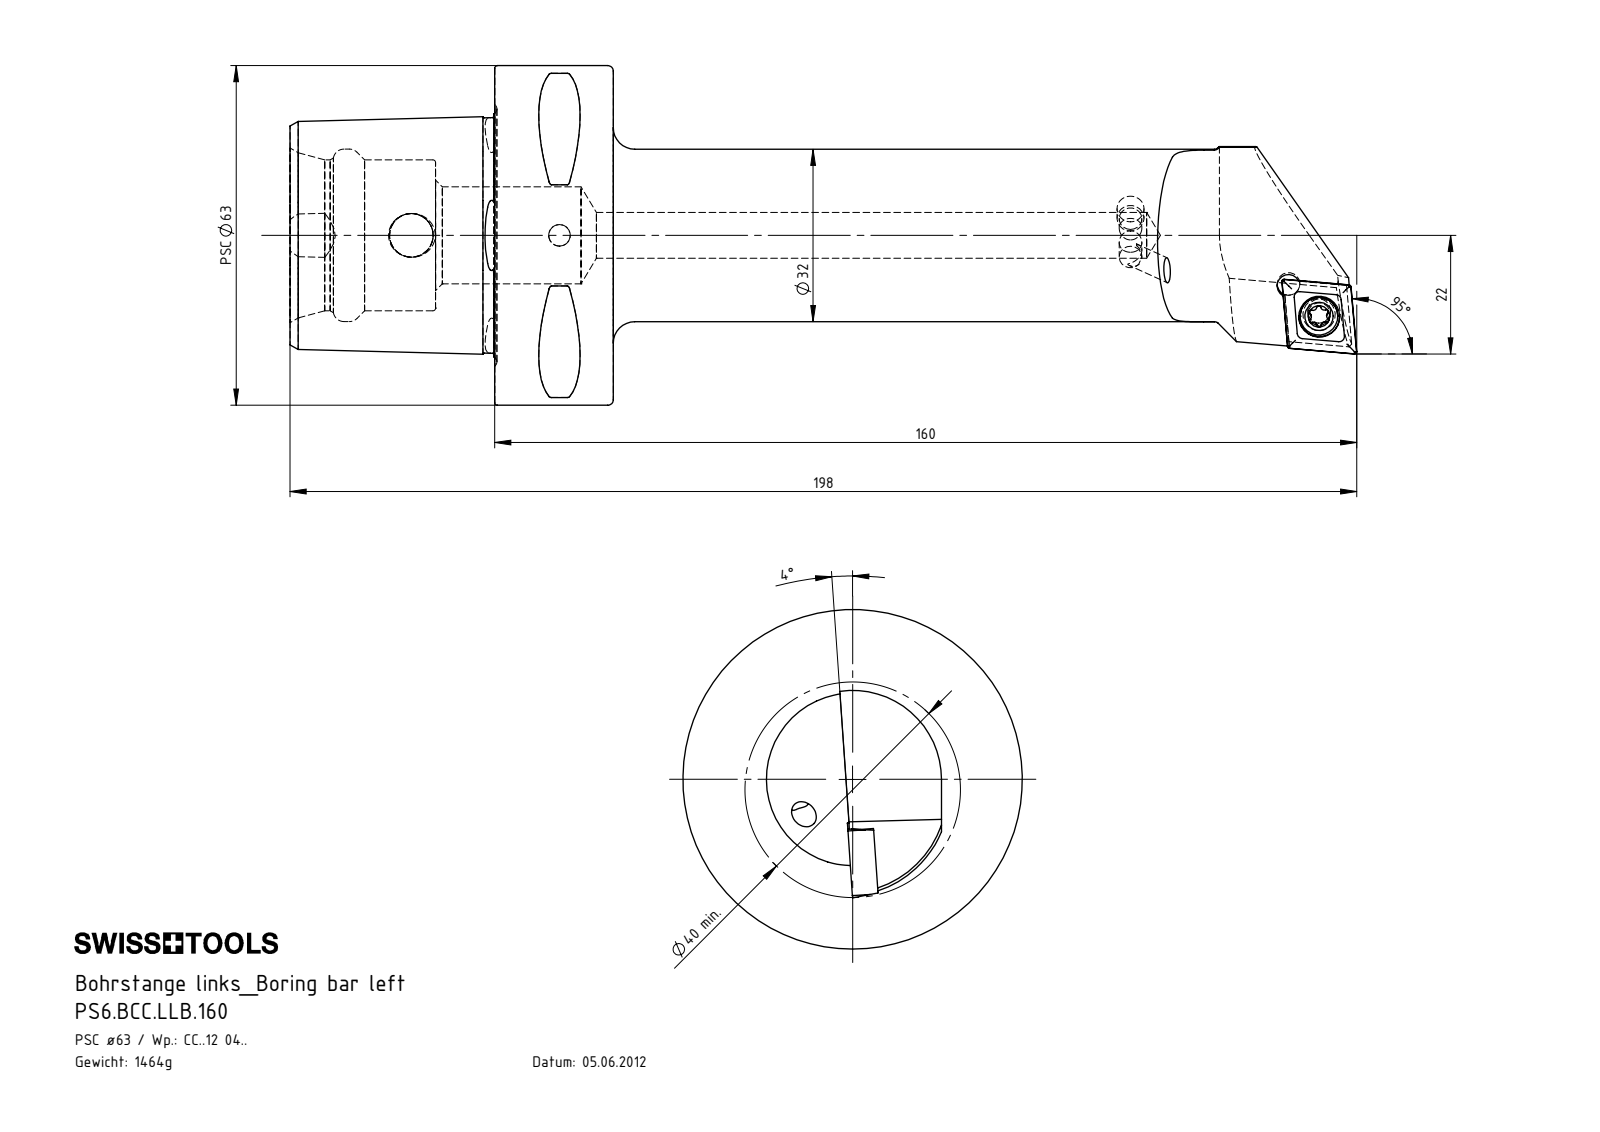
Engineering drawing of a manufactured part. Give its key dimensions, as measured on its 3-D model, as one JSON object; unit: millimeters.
{"part_name": "WCC-ER2.001.010_A; CCMT120404; PS6-BCC.LLB.160_A; PS6.BCC.LLB.160 (+1 more)", "step_written_by": "SolidWorks 2017 (AUTOMOTIVE_DESIGN)", "units": "millimeters", "bodies": {"solids": 5, "faces": 282, "planar": 49, "cylindrical": 75, "other": 158}, "overall_size": [198, 63, 63], "volume_mm3": 187408, "surface_area_mm2": 36921, "round_holes": [[4.2, 4], [4, 2], [5.5, 1], [7.6, 1], [8.1, 1], [8.5, 1], [18, 1], [28, 1], [32, 1]], "round_bosses_or_shafts": [[5, 2], [63, 1], [7, 1]], "partial_cylinders_radius": [[0.5, 8], [0.39, 6], [0.69, 3], [0.69, 3], [3, 1], [6, 1], [16.5, 1], [19, 1]], "face_to_face_distances": [22, 38, 60, 24.88, 27, 11, 33, 4.46, 55.8, 37.8], "hole_center_spacings": [8.01, 8.09, 27.5]}
